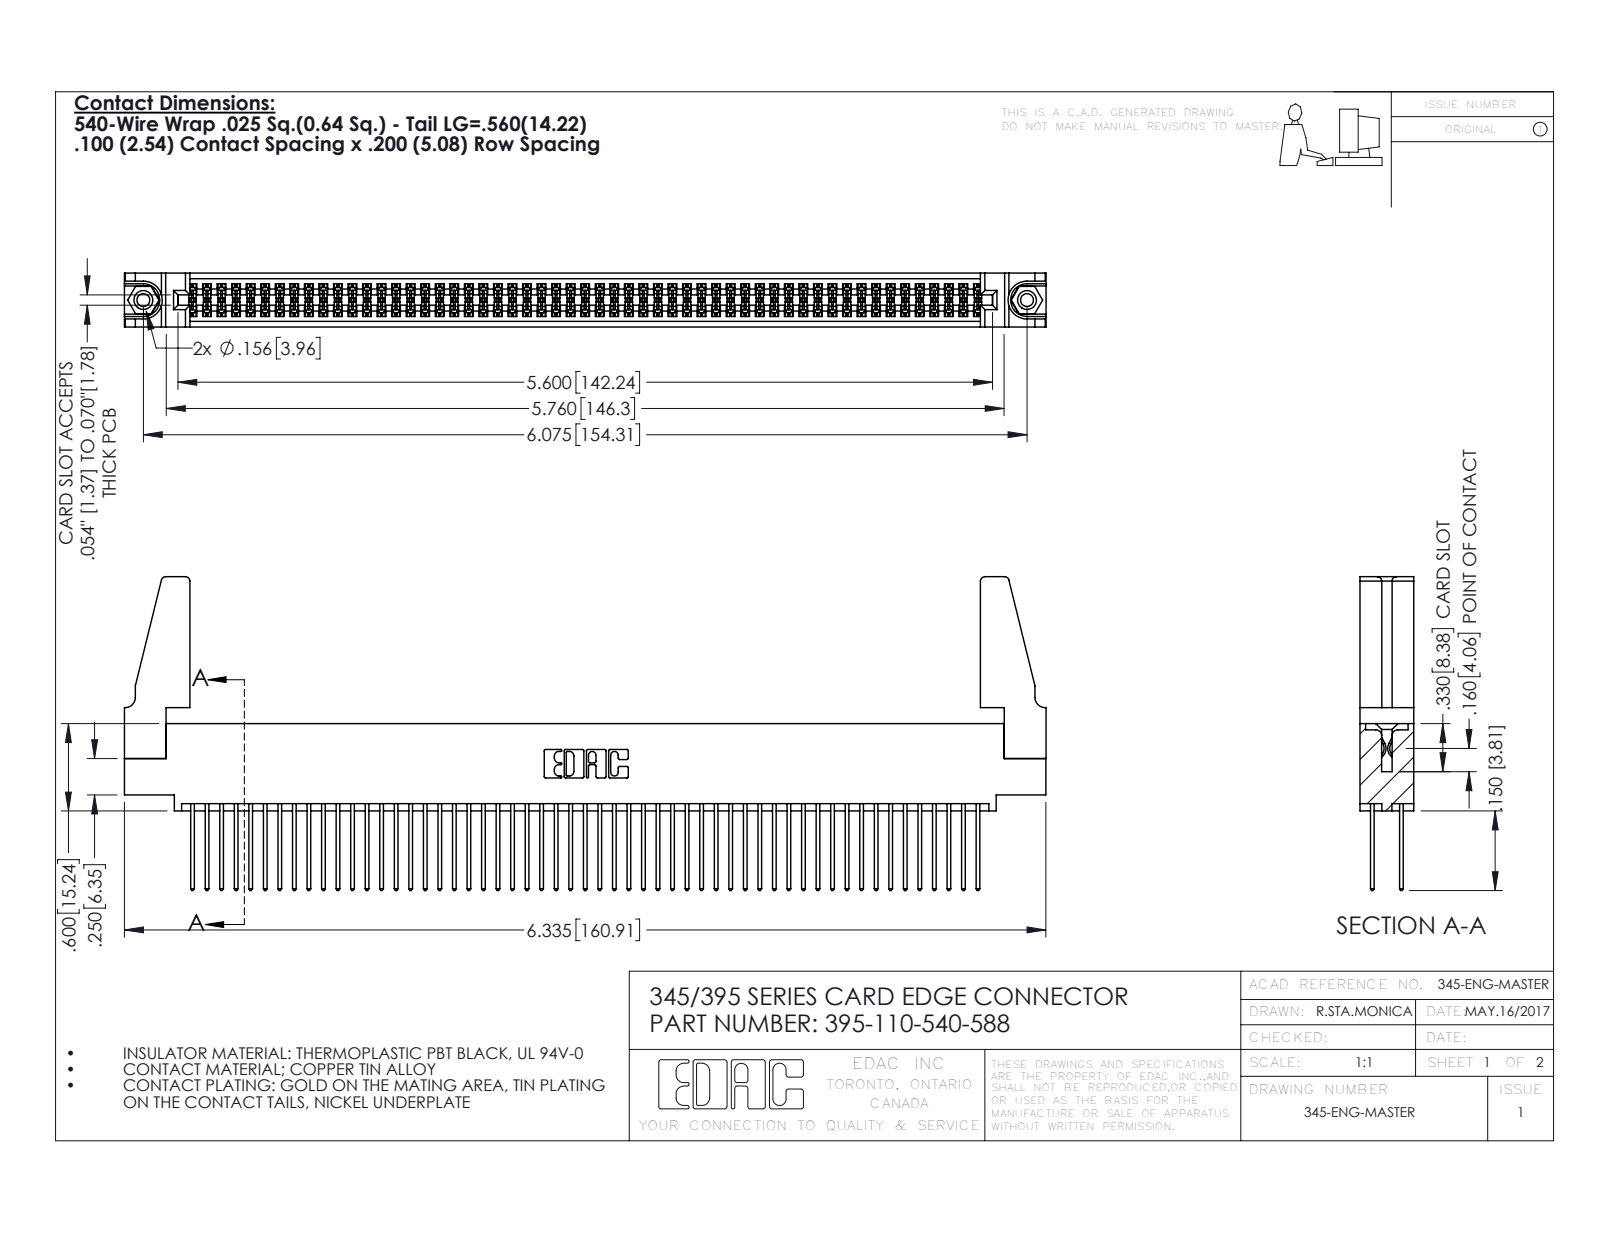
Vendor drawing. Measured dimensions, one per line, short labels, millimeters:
name: 345 Part_0.110 Offset - 0.156 Dia-TH; 345-292-001_345-293-140; 345-250-001_345-250-001-102; 395-110-540-588 (+1 more)
written by: SolidWorks 2016 (CONFIG_CONTROL_DESIGN)
unit: mm
bodies: 115 solids, 5754 faces (3786 planar, 1952 cylindrical, 16 other)
size: 160.9 × 54.8 × 9.4
volume: 19 350 mm³; area: 29 190 mm²
holes: 2× ⌀2.3, 2× ⌀3.2, 2× ⌀4, 1× ⌀1.6
bosses: 2× ⌀3.9
rounds: 165× R0.2, 110× R0.3, 22× R0.3, 8× R0.8, 6× R0.2, 6× R0.8, 3× R0.7, 2× R0.4
face distances: 1.8, 7.6, 5.1, 2.5, 6.9, 0.6, 9.4, 5.7, 4.4, 3.8
hole spacings: 6.9, 148.3, 154.3
